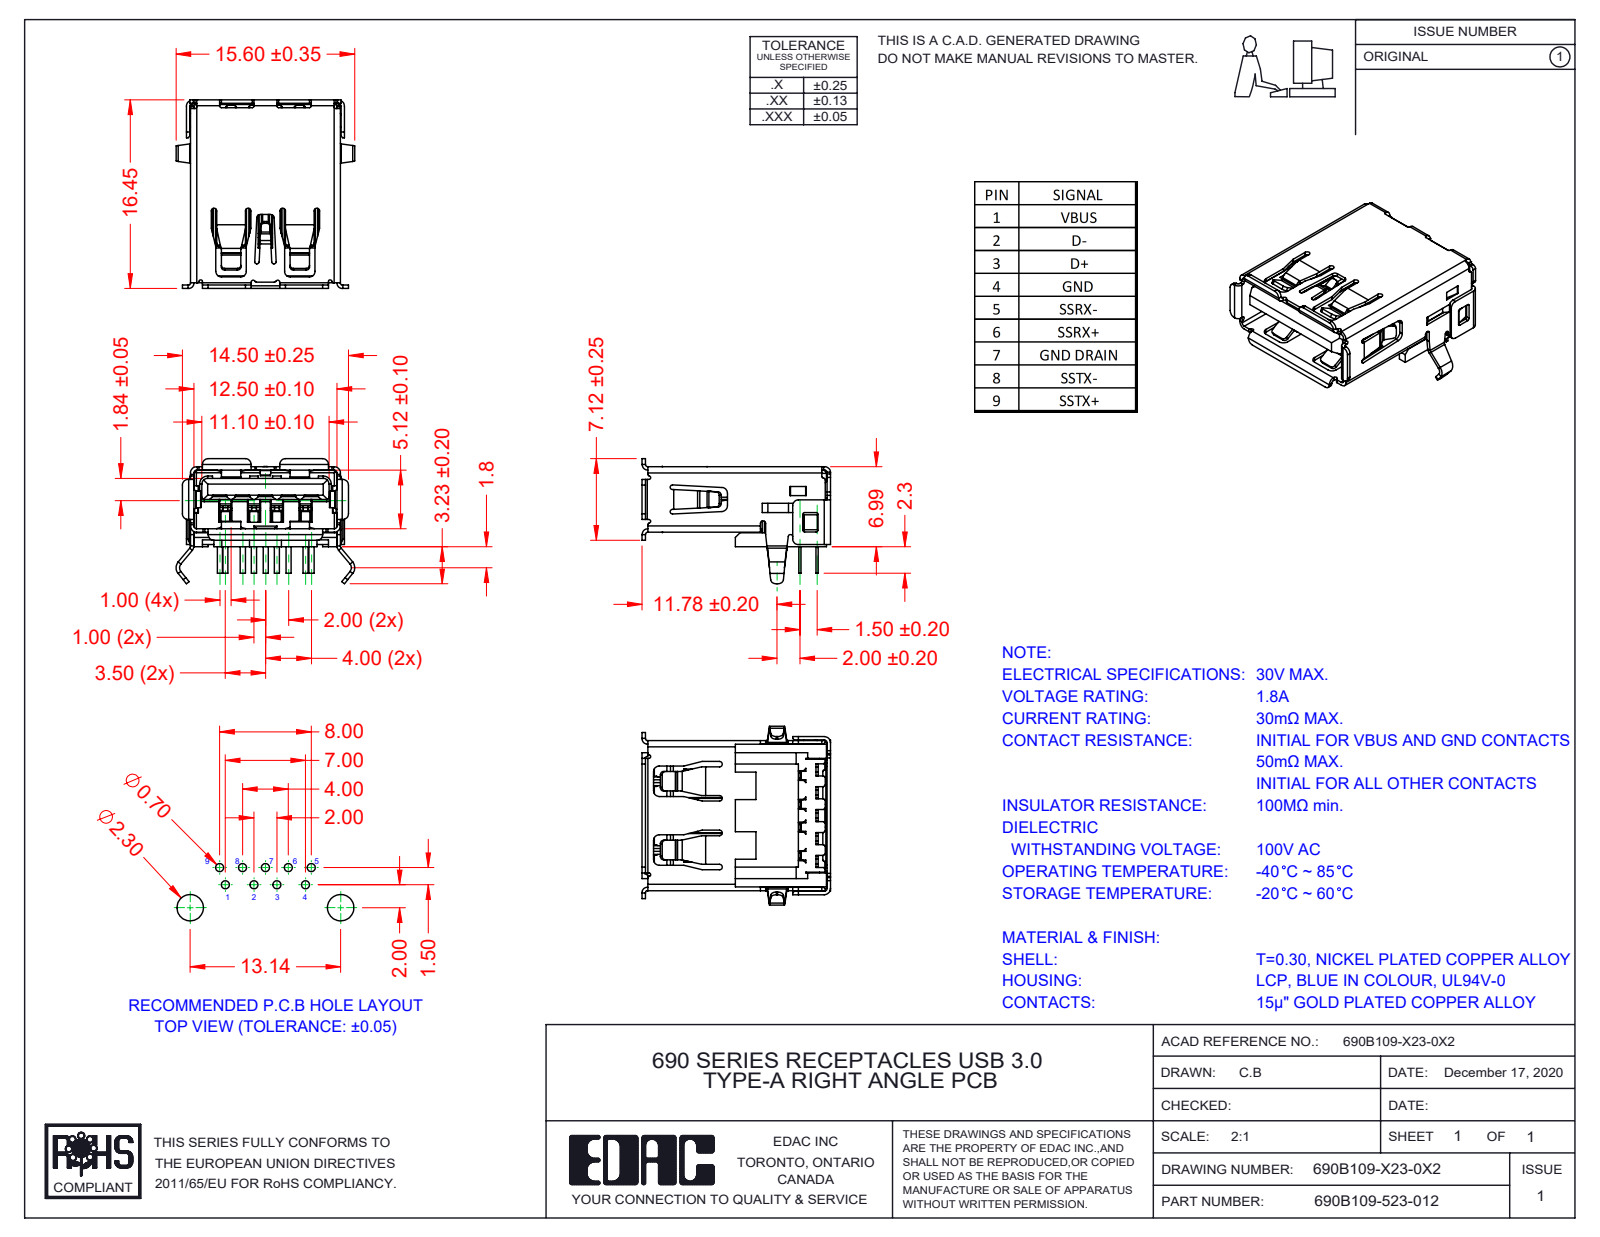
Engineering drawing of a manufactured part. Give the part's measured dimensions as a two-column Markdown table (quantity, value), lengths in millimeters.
| quantity | value |
| --- | --- |
| part name | Insulator 690B109-X23-0X2; Shell 690B109-X23-0X2; Contacts 690B109-X23-0X2; 690B109-123-012 |
| STEP written by | SolidWorks 2020 (AUTOMOTIVE_DESIGN) |
| units | millimeters |
| bodies | 11 solids, 2295 faces (1564 planar, 593 cylindrical, 138 other) |
| overall size | 16.45 × 15.6 × 10.92 |
| volume | 677 mm³ |
| surface area | 3 042 mm² |
| partial cylindrical surfaces (radius × count) | 0.15 × 103, 0.3 × 46, 0.2 × 35, 0.5 × 33, 0.1 × 16, 0.45 × 12, 0.11 × 8, 0.25 × 8 |
| main face-to-face distances | 5.42, 1.02, 0.35, 12.8, 4.7, 2.56, 2.86, 1.27, 0.72, 1.84 |
